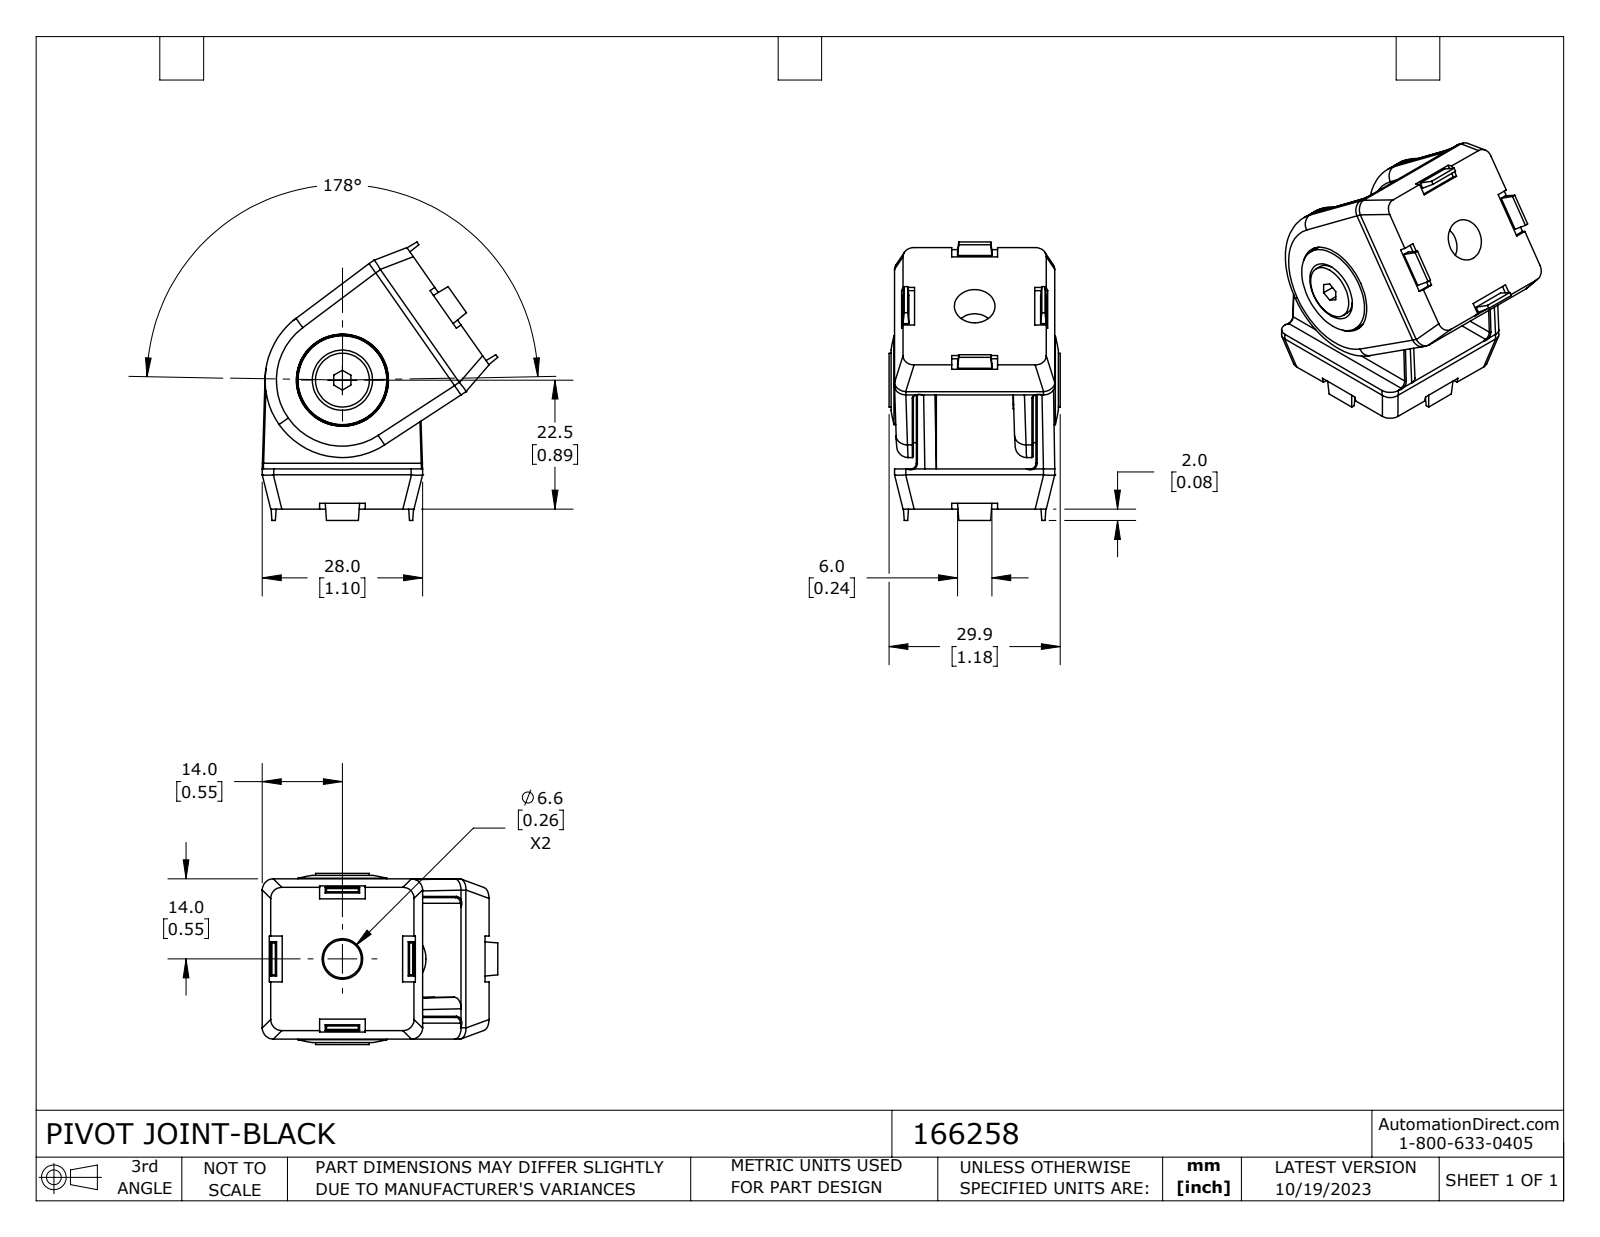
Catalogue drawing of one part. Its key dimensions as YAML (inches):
part_name: "166258"
step_written_by: "SolidWorks 2023 (CONFIG_CONTROL_DESIGN)"
units: inches
bodies: {solids: 8, faces: 487, planar: 200, cylindrical: 123, other: 164}
overall_size: [1.914, 1.619, 1.177]
volume: 1.144
surface_area: 20.85
round_holes:
  - {diameter: 0.098, count: 4}
  - {diameter: 0.165, count: 1}
  - {diameter: 0.295, count: 1}
  - {diameter: 0.559, count: 1}
  - {diameter: 0.866, count: 1}
round_bosses_or_shafts:
  - {diameter: 1.063, count: 1}
  - {diameter: 0.858, count: 1}
  - {diameter: 0.61, count: 1}
  - {diameter: 0.551, count: 1}
  - {diameter: 0.441, count: 1}
  - {diameter: 0.394, count: 1}
  - {diameter: 0.37, count: 1}
  - {diameter: 0.197, count: 1}
partial_cylinders:
  - {radius: 0.079, count: 24}
  - {radius: 0.008, count: 17}
  - {radius: 0.039, count: 4}
  - {radius: 0.048, count: 4}
face_to_face_distances: [0.02, 0.803, 0.276, 0.039, 0.843, 0.823, 0.815, 0.783, 0.138, 0.118]
hole_center_spacings: [0.354, 0.327, 0.628, 0.708, 0.709]
